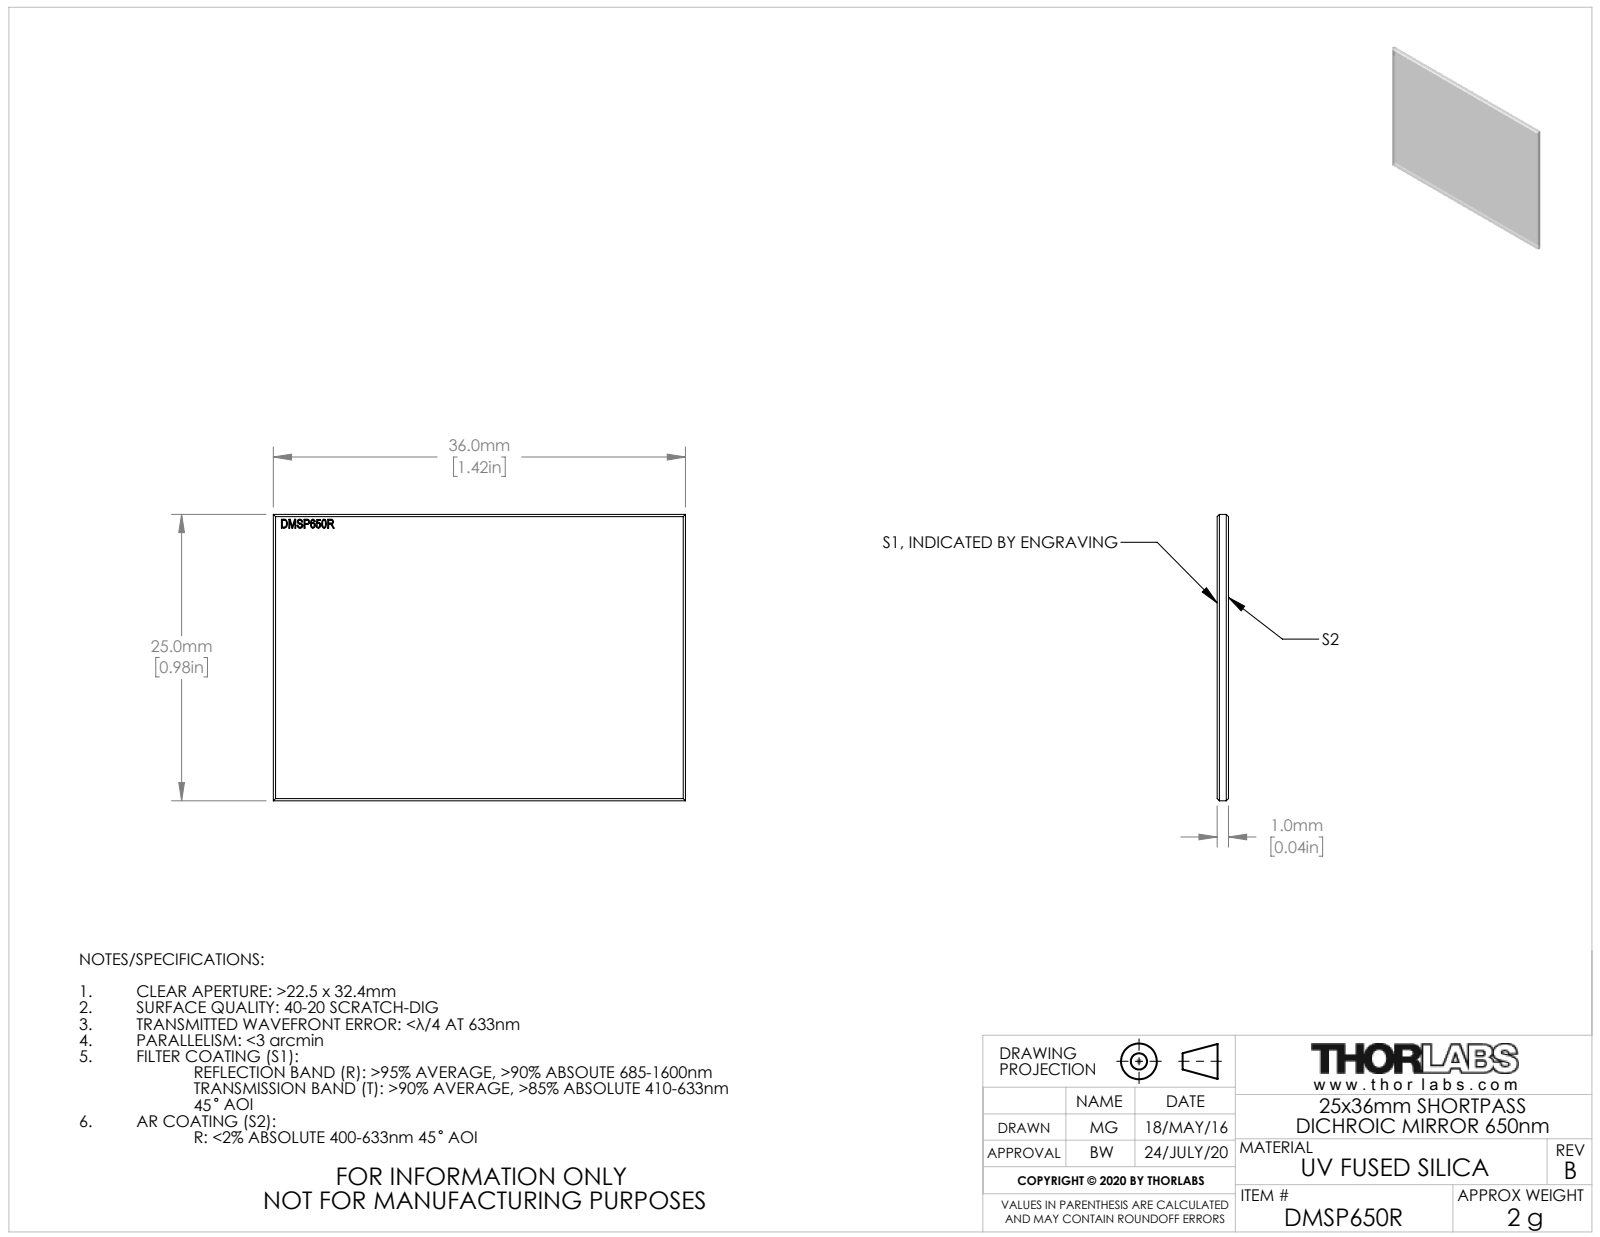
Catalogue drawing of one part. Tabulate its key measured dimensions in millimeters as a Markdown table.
| quantity | value |
| --- | --- |
| part name | TTN045183-E0W |
| STEP written by | SolidWorks 2018 (CONFIG_CONTROL_DESIGN) |
| units | millimeters |
| bodies | 1 solid, 141 faces (76 planar, 0 cylindrical, 65 other) |
| overall size | 36 × 25 × 1 |
| volume | 895 mm³ |
| surface area | 1 894 mm² |
| main face-to-face distances | 1, 25, 18.1, 36, 25.88, 0.99, 0.72, 1.97, 0.8, 0.53 |
